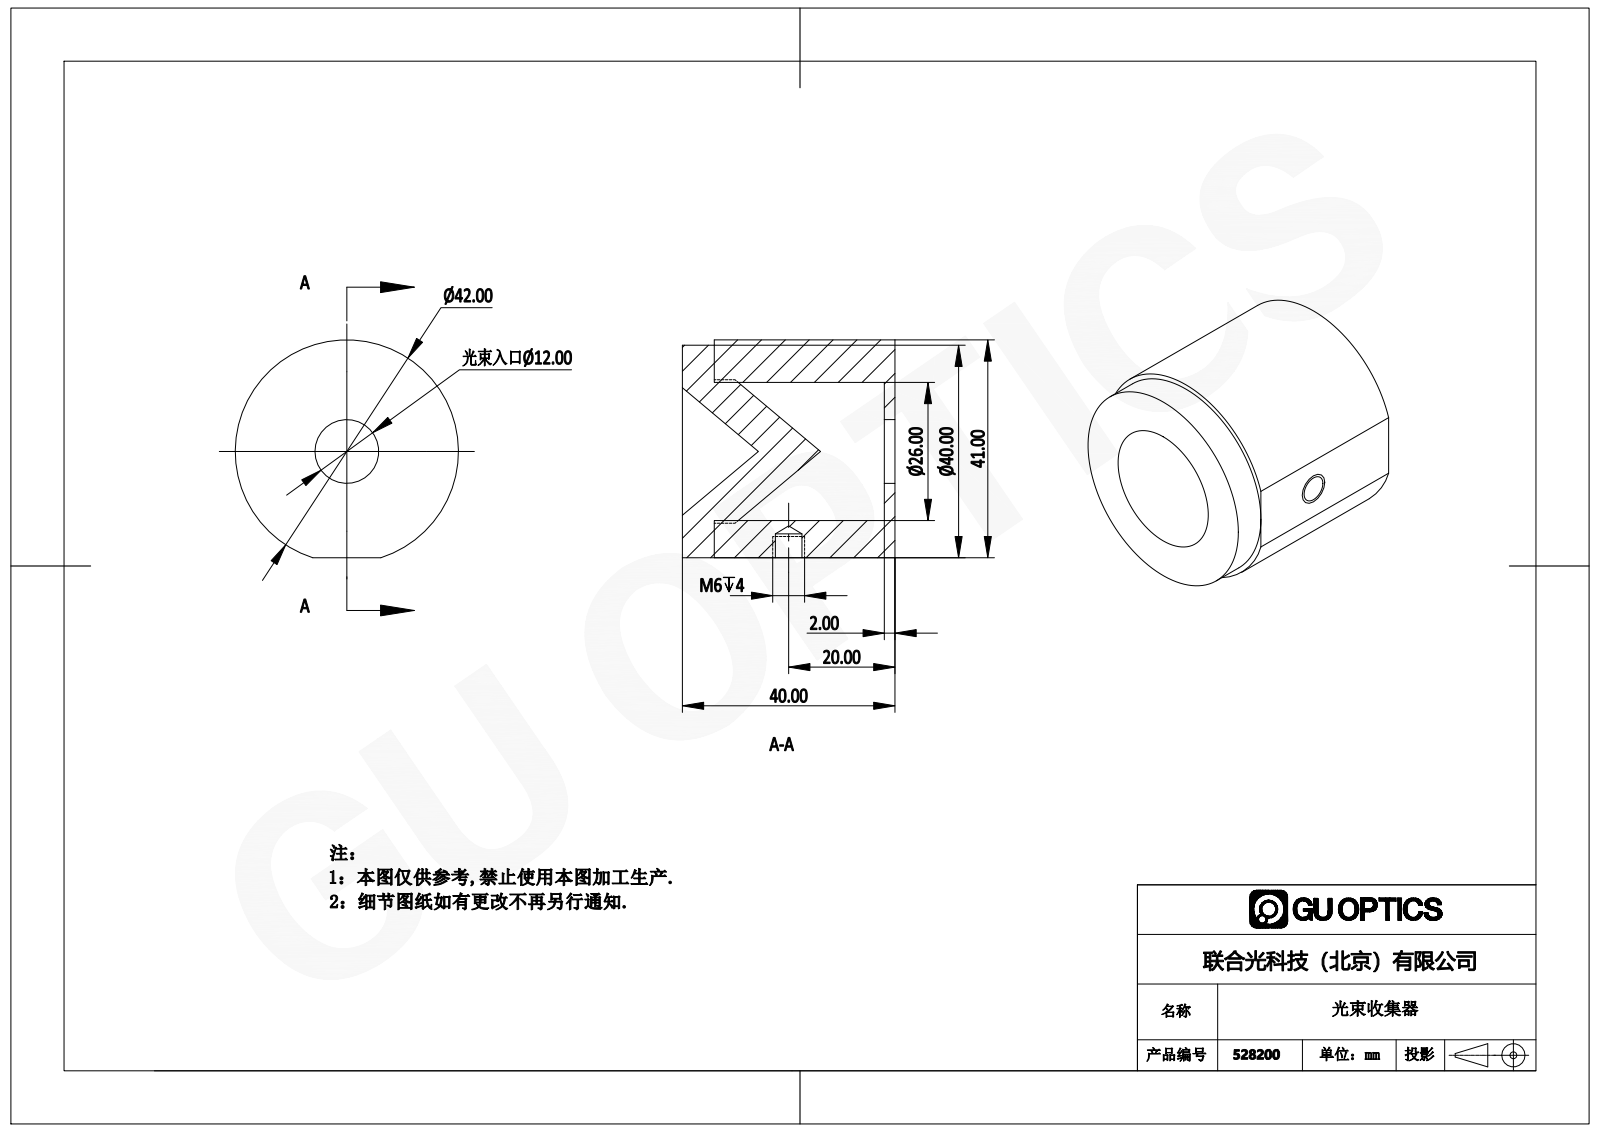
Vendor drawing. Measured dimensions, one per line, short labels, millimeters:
name: 528200
written by: SolidWorks 2020 (AUTOMOTIVE_DESIGN)
unit: mm
bodies: 1 solid, 21 faces (5 planar, 10 cylindrical, 6 other)
size: 42 × 41 × 40
volume: 40 014 mm³; area: 11 765 mm²
holes: 1× ⌀5, 1× ⌀12, 1× ⌀26
bosses: 1× ⌀42, 1× ⌀40
face distances: 40, 2, 38, 34, 32, 6
